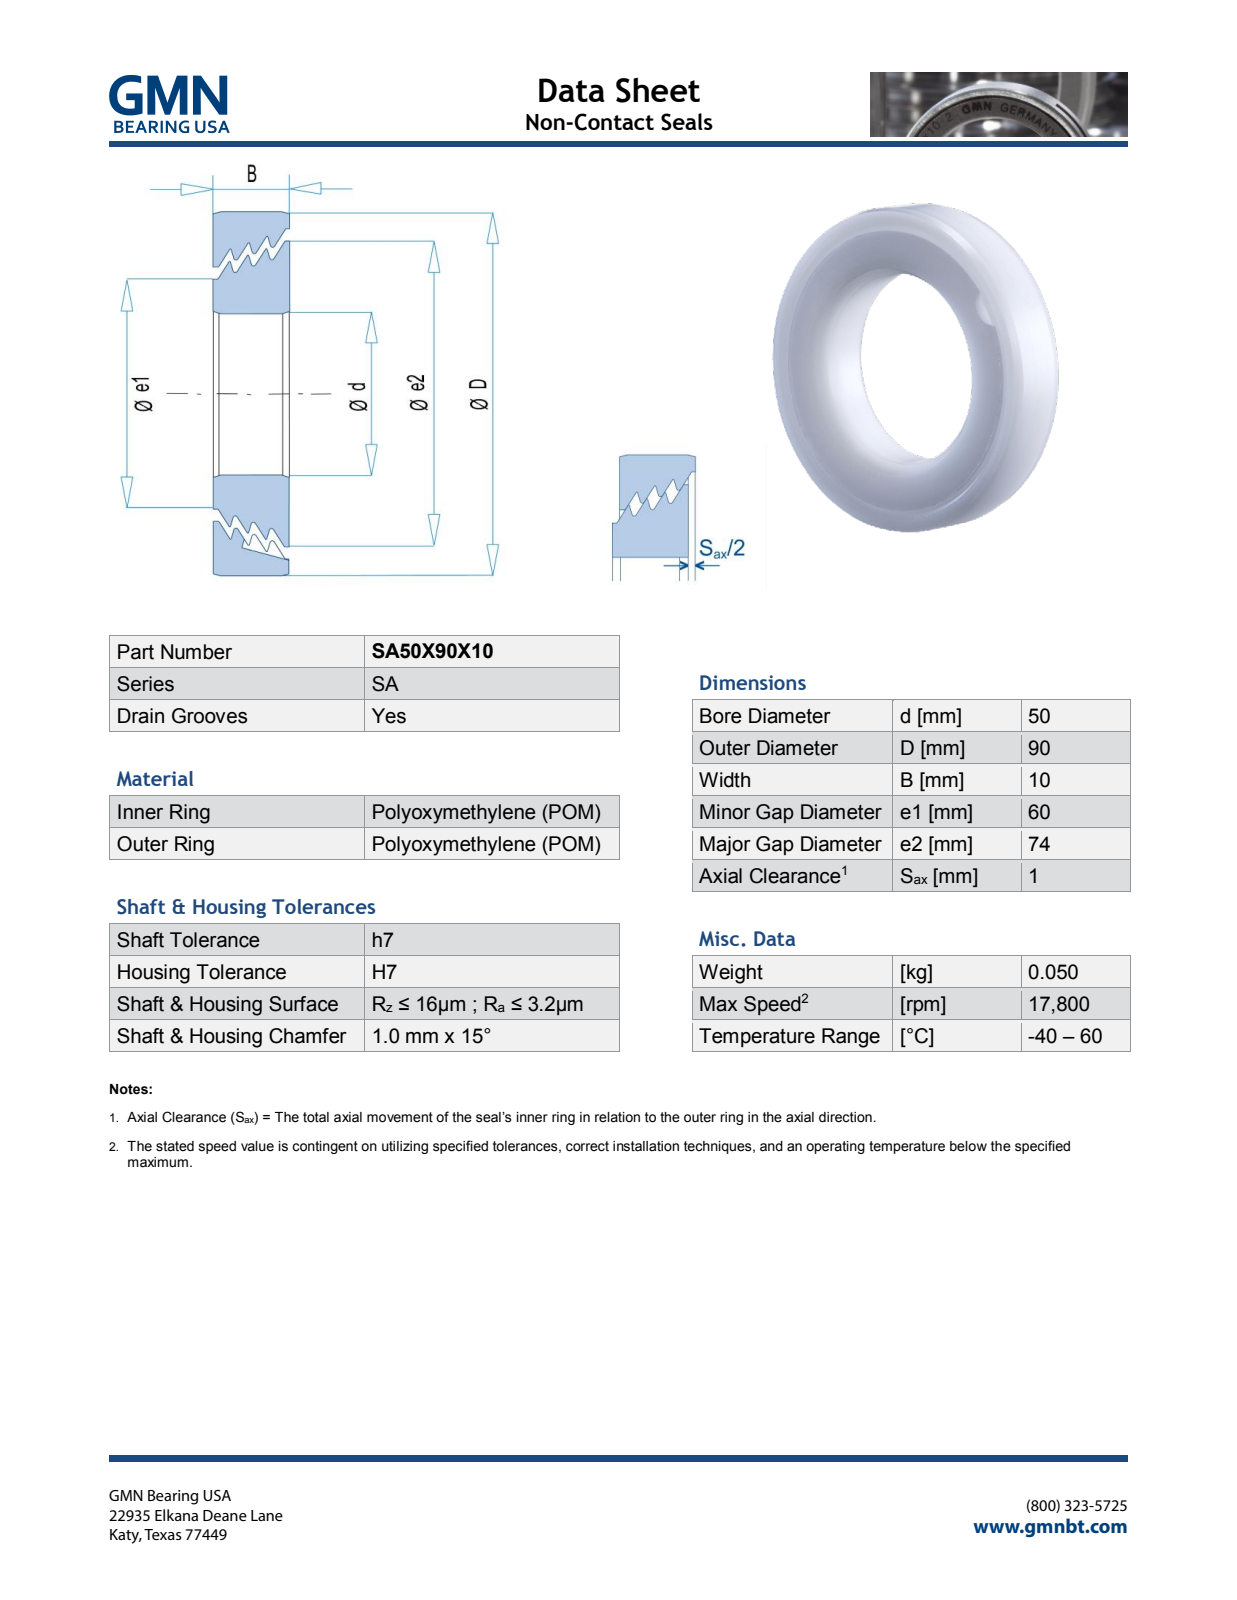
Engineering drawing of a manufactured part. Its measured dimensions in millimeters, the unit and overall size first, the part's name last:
Units: millimetres
Overall size (bounding box): 90 × 90 × 10.07
Round holes (diameter × count): ⌀50 ×1, ⌀61.63 ×1, ⌀75.63 ×1
Round bosses / shafts (diameter × count): ⌀90 ×1, ⌀74 ×1, ⌀60 ×1
Partial cylindrical surfaces — rounded edges, fillets, slot ends (radius × count): R6 ×1
Main face-to-face distances: 10, 10.07, 5.46, 5.39, 4.61, 0.42, 3.33, 0.41, 2.91, 2.36
Volume: 42 080 mm³ · Surface area: 21 144 mm²
Bodies: 2 solids, 695 faces (622 planar, 13 cylindrical, 60 other)
Part name (STEP PRODUCT): SA50X90X10_PRT
STEP written by: PRO/ENGINEER BY PARAMETRIC TECHNOLOGY CORPORATION, 2013150 (AUTOMOTIVE_DESIGN)
